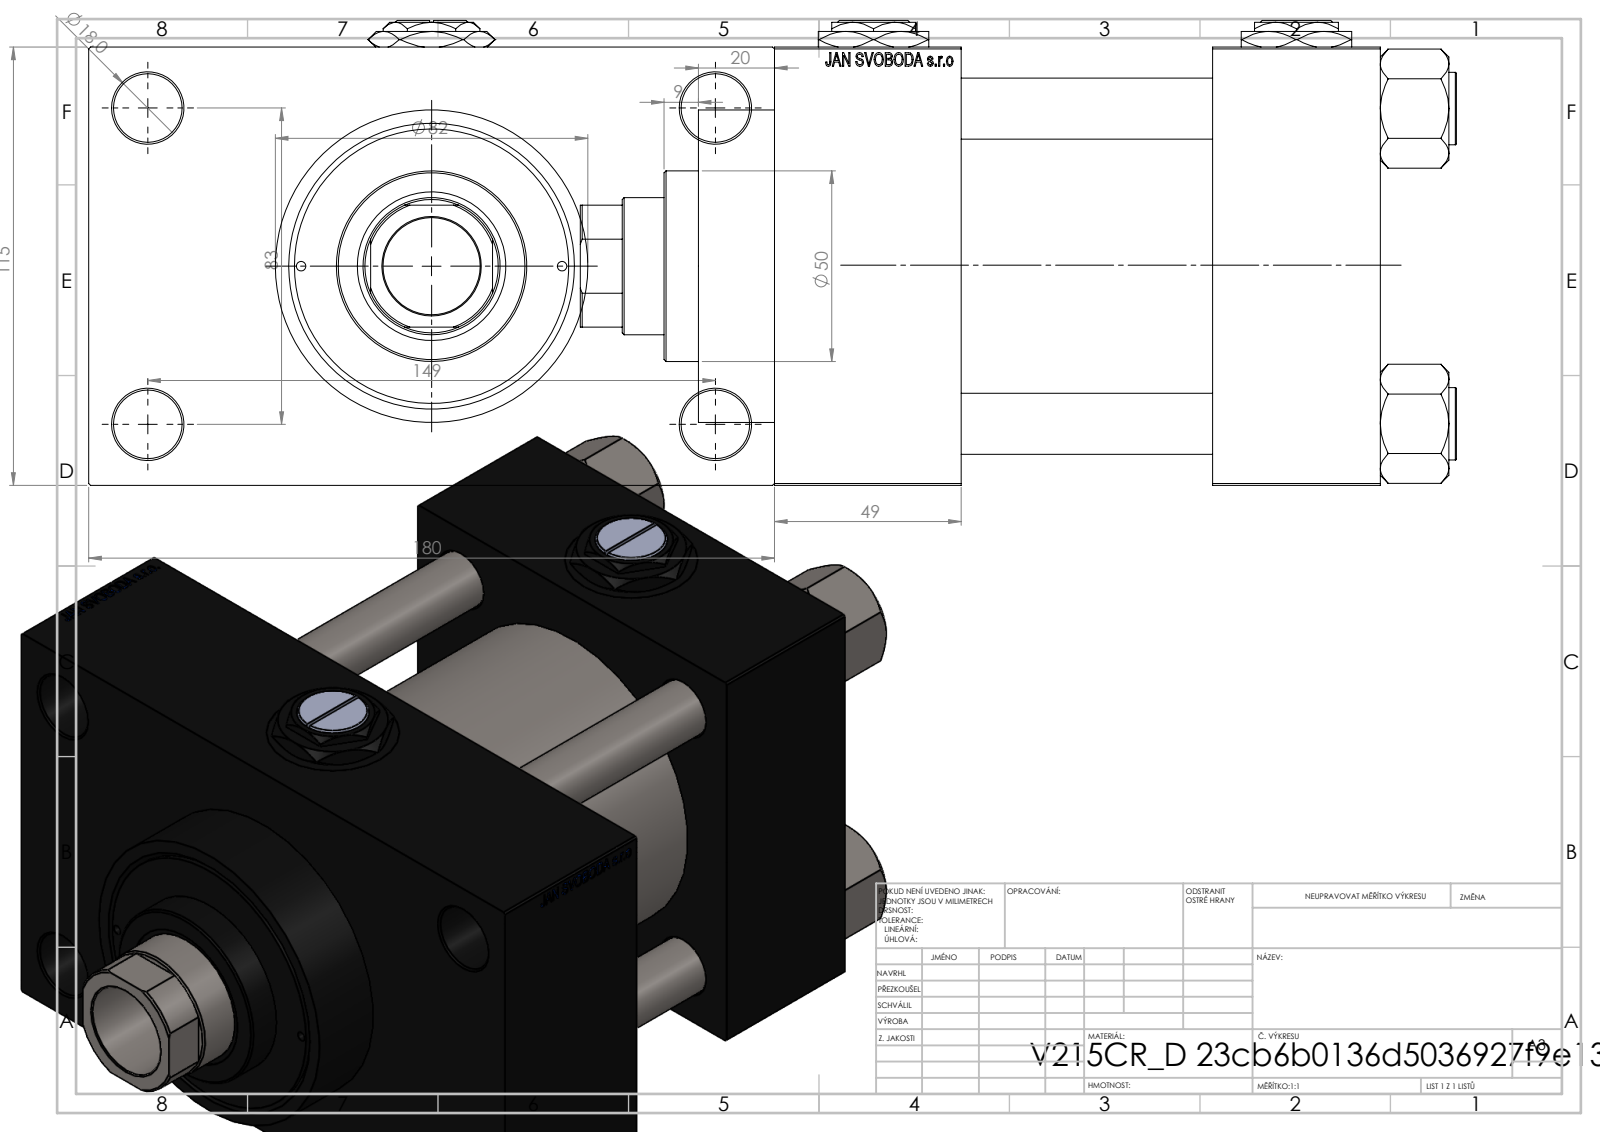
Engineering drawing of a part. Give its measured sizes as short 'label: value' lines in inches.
name: V215CR_D_TYCINKA; V215CR_D_Body; V215CR_VCP_D; NUT_M5_D (+2 more)
written by: SolidWorks 2019 (CONFIG_CONTROL_DESIGN)
unit: in
bodies: 13 solids, 1260 faces (595 planar, 103 cylindrical, 562 other)
size: 9.055 × 7.087 × 4.803
volume: 119.9 in³; area: 469.9 in²
holes: 4× ⌀0.63, 4× ⌀0.709, 4× ⌀1.041, 4× ⌀1.378, 3× ⌀0.276, 2× ⌀0.098, 1× ⌀1.004, 1× ⌀1.417, 1× ⌀1.535, 1× ⌀2.402, 1× ⌀2.835, 1× ⌀3.15
bosses: 4× ⌀0.748, 1× ⌀3.386, 1× ⌀3.228, 1× ⌀1.969
rounds: 1× R0.689
face distances: 4.528, 2.598, 4.331, 1.929, 1.732, 6.26, 1.28, 5.807, 0.787, 2.717
hole spacings: 1.305, 1.652, 2.276, 2.302, 3.256, 3.357, 3.393, 3.513
